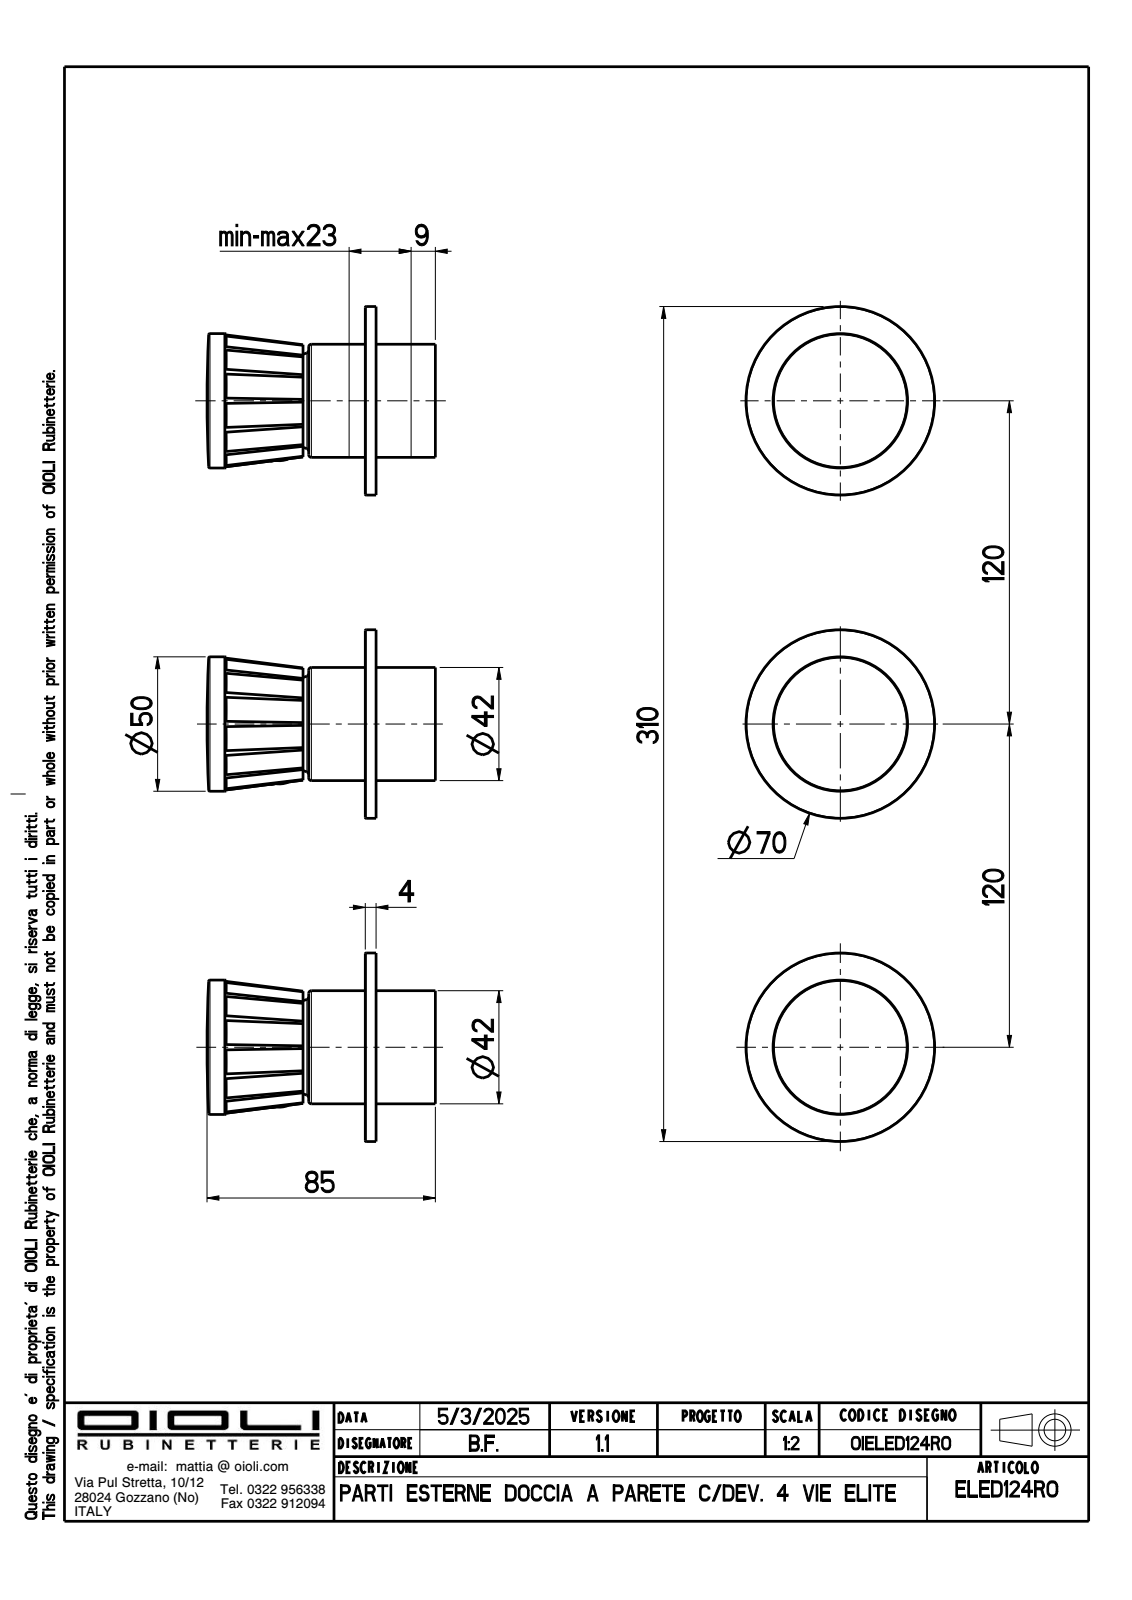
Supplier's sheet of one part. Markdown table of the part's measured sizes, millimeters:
| quantity | value |
| --- | --- |
| part name | OIBR00949; OIBR00242; OIBR00948; OIAQ00013 (+2 more) |
| STEP written by | CREO PARAMETRIC BY PTC INC, 2024493 (CONFIG_CONTROL_DESIGN) |
| units | millimeters |
| bodies | 15 solids, 471 faces (183 planar, 144 cylindrical, 144 other) |
| overall size | 310 × 84.72 × 70 |
| volume | 132 470 mm³ |
| surface area | 111 062 mm² |
| round holes (diameter × count) | 9.5 × 3, 30 × 3, 39.5 × 3, 40 × 3, 42.6 × 3, 45.5 × 3, 4 × 1, 4.2 × 1, 5.3 × 1, 6.5 × 1 |
| round bosses / shafts (diameter × count) | 70 × 3, 49.9 × 3, 42 × 3, 16.5 × 3, 5 × 1 |
| partial cylindrical surfaces (radius × count) | 0.1 × 22, 6.8 × 6 |
| main face-to-face distances | 4, 59.6, 55.6, 119.04, 2.1, 13, 17, 42.6, 24.1, 22 |
| hole center spacings | 120, 240 |
